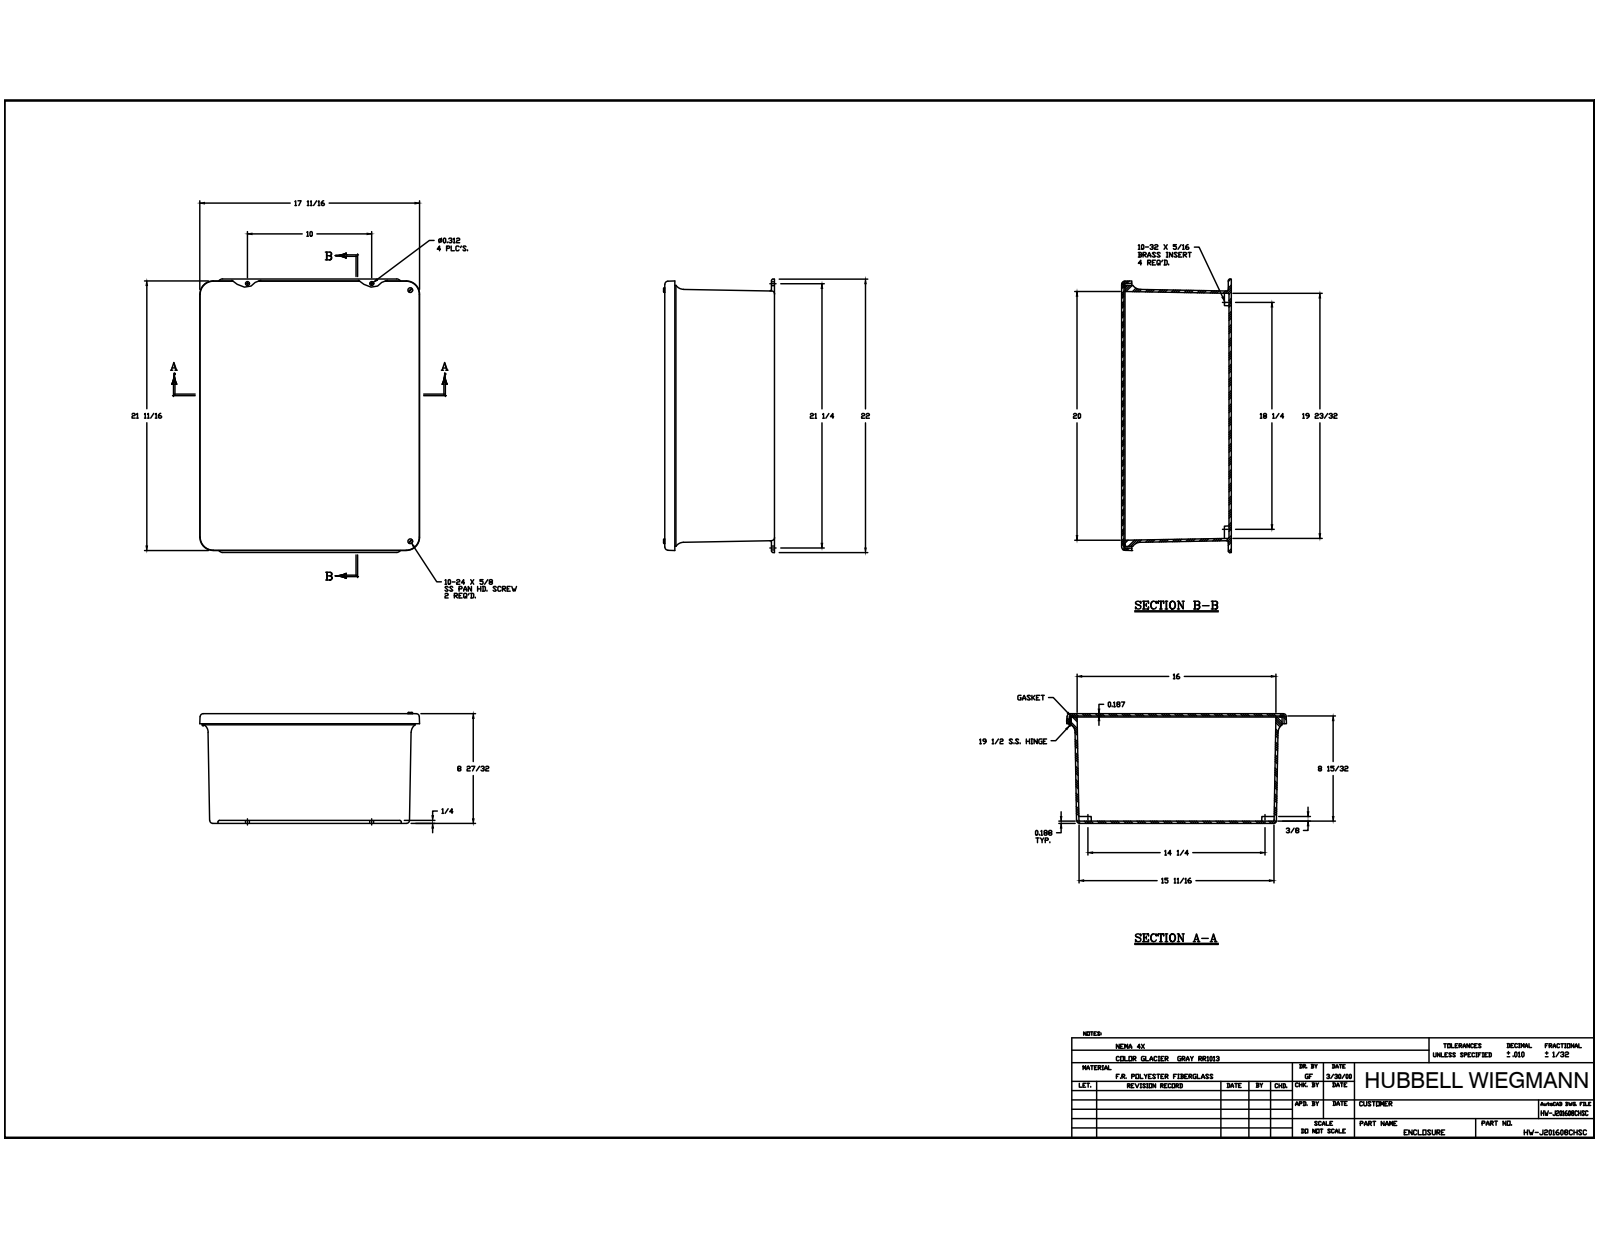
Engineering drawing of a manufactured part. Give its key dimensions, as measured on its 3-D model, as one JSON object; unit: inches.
{"part_name": "J2016HW_1; RMINS45821P_9; RMINS45821P_10; RMINS45821P_11 (+8 more)", "step_written_by": "Autodesk Inventor 2014 (AUTOMOTIVE_DESIGN)", "units": "inches", "bodies": {"solids": 26, "faces": 985, "planar": 393, "cylindrical": 387, "other": 205}, "overall_size": [22, 17.711, 8.96], "volume_in3": 282.9, "surface_area_in2": 2939, "round_holes": [[0.131, 12], [0.14, 12], [0.152, 5], [0.156, 4], [0.218, 4], [0.145, 2], [0.085, 1]], "round_bosses_or_shafts": [[0.25, 12], [0.125, 12], [0.27, 6], [0.19, 2], [0.156, 2], [0.155, 1]], "partial_cylinders_radius": [[0.031, 20], [0.125, 10], [0.25, 8], [0.2, 7], [0.063, 4], [0.375, 4], [0.75, 4]], "face_to_face_distances": [0.187, 8.642, 8.829, 0.188, 8.454, 8.641, 0.313, 0.5, 8.563, 8.375], "hole_center_spacings": [3.75, 7.5, 0.25, 3.5, 4, 7.25, 7.75, 11]}
